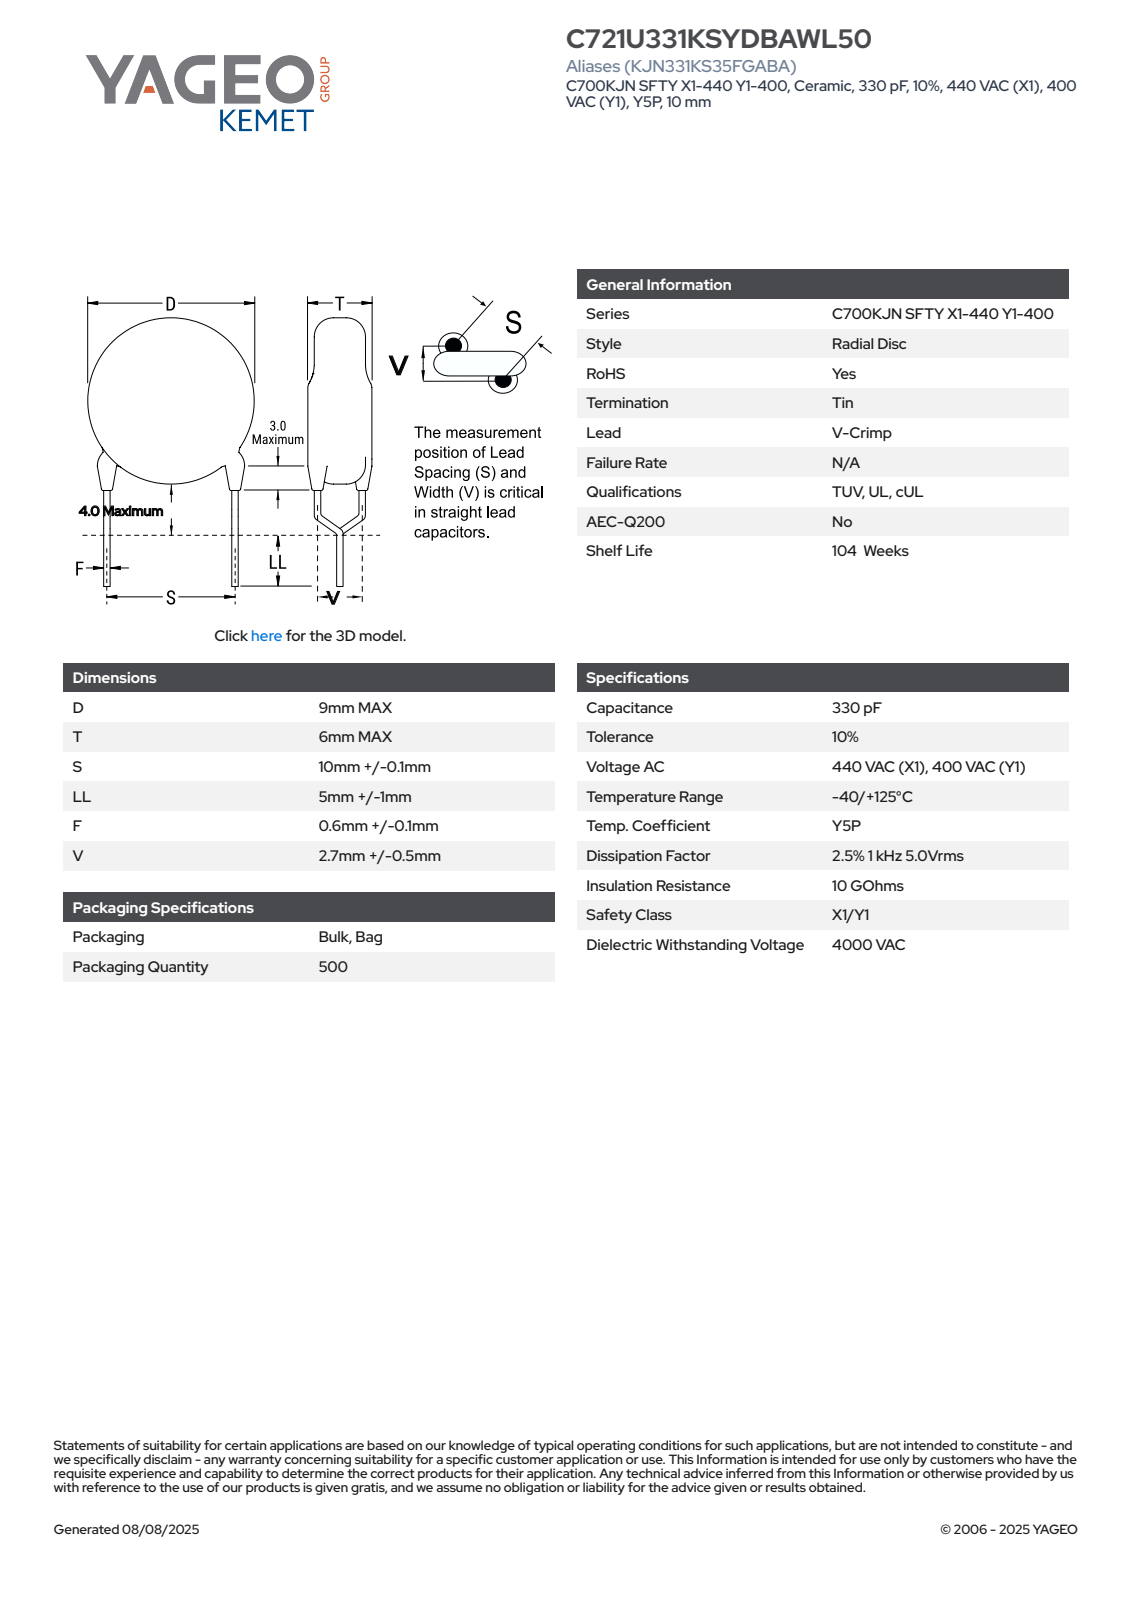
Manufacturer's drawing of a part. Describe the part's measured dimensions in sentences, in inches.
The part is named "CCD_VC9X6_D9T6S10LL6F0.7V2.7". Its 3-D file was written by "SolidWorks 2021 (AUTOMOTIVE_DESIGN)". It is 4 solids with 89 faces: 63 planar, 22 cylindrical and 4 other. Overall it measures 0.591 by 0.441 by 0.236 inches. Its volume is 0.023 cubic inches and its surface area 0.512 square inches. Round bosses or shafts: 6 of diameter 0.028, 4 of diameter 0.047, 1 of diameter 0.354. The main face-to-face distances are 0.236, 0.043, 0.442, 0.206, 0.398, 0.162, 0.035, 0.027, 0.088, 0.083.
